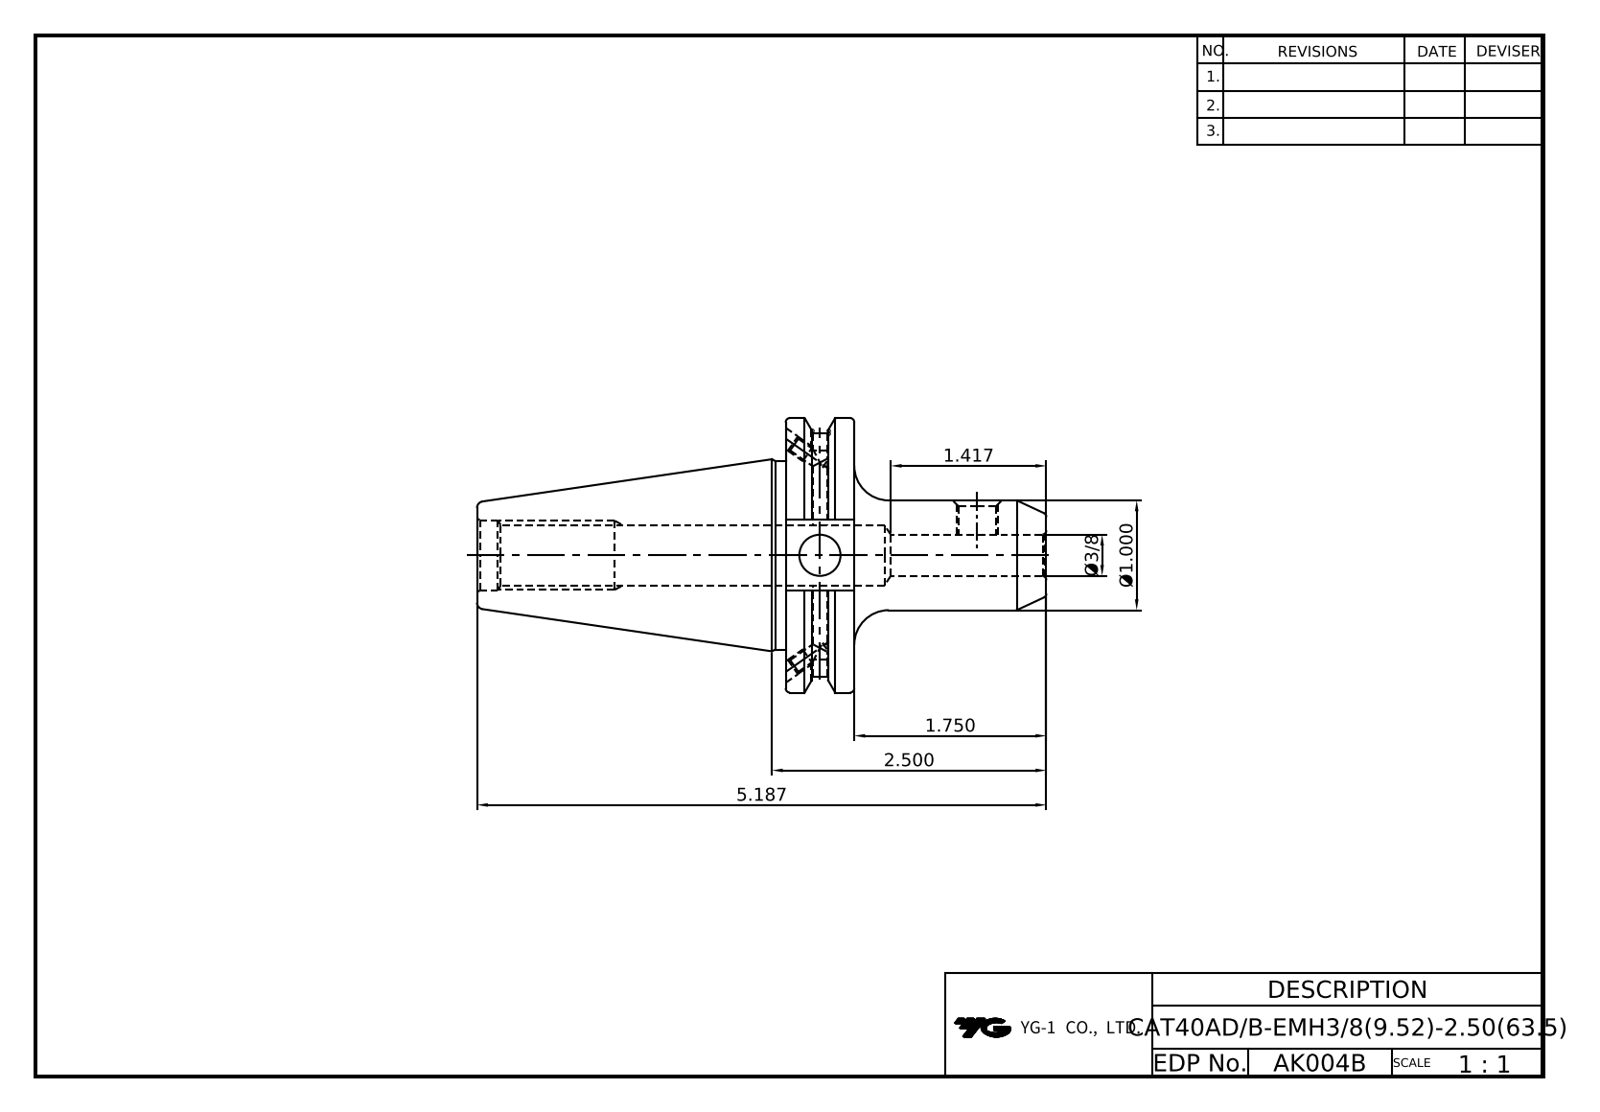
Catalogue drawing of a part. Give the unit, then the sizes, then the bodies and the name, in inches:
Units: inches
Overall size (bounding box): 5.187 × 2.5 × 2.405
Round holes (diameter × count): ⌀0.128 ×4, ⌀0.157 ×2, ⌀0.165 ×2, ⌀0.375 ×2, ⌀0.33 ×1, ⌀0.527 ×1, ⌀0.642 ×1
Round bosses / shafts (diameter × count): ⌀2.5 ×1, ⌀1.717 ×1, ⌀1 ×1
Partial cylindrical surfaces — rounded edges, fillets, slot ends (radius × count): R1.108 ×1
Main face-to-face distances: 0.625, 1.874, 0.645, 2.812, 3.437, 5.187, 2.375, 1.75, 3.05, 0.238
Volume: 7.243 in³ · Surface area: 39.62 in²
Bodies: 1 solid, 85 faces (35 planar, 27 cylindrical, 23 other)
Part name (STEP PRODUCT): LO-CAT40ADB-EMH9.525-63.5
STEP written by: Autodesk Inventor 2025 (AUTOMOTIVE_DESIGN)
